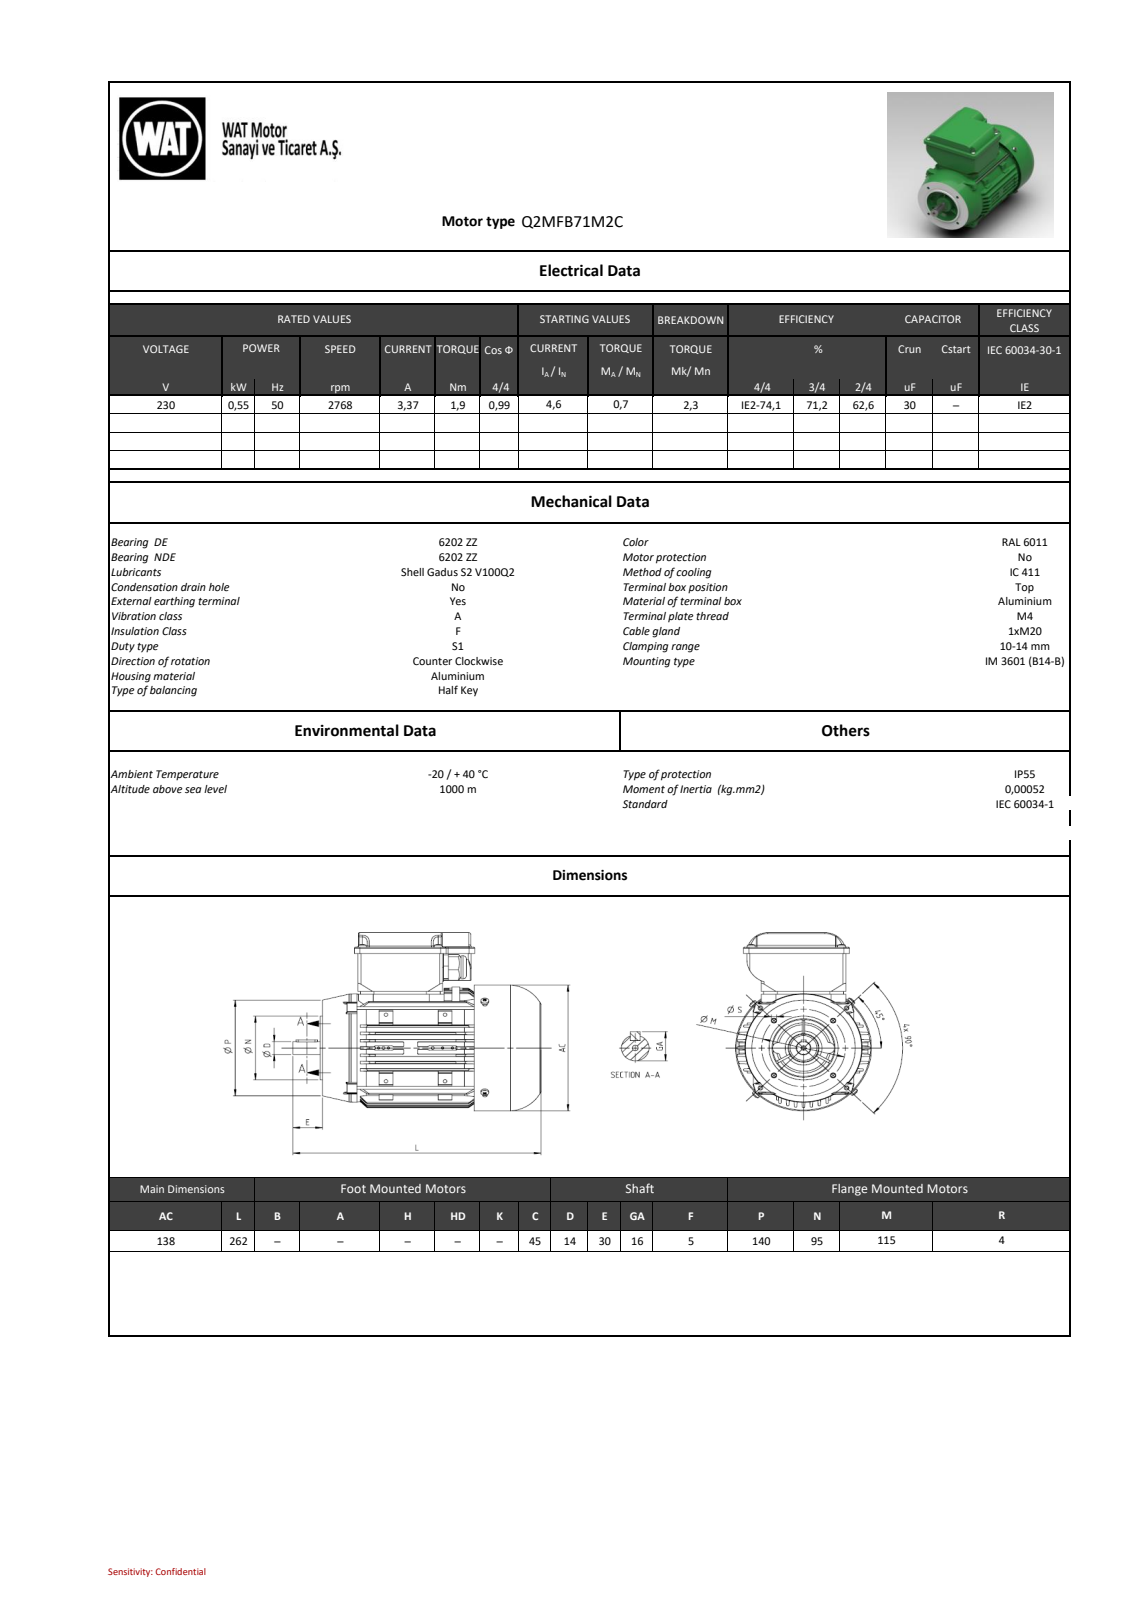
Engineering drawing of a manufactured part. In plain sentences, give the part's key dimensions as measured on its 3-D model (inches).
The part is named "BY6434017xx_004-TK_QM63-80; BY6424130xx_004-TKK_QM63-80; BY6422457xx_005-MOTOR_KAPAGI_QS71FB_ISLEME; 641304741_AZ-KAMA PARALEL A 5x5x22 St50 DIN6885 (+6 more)". Its 3-D file was written by "SIEMENS PLM Software NX2206.8101 (AUTOMOTIVE_DESIGN)". It is 24 solids with 2559 faces: 1236 planar, 703 cylindrical and 620 other. Overall it measures 10.315 by 7.746 by 5.531 inches. Its volume is 48.03 cubic inches and its surface area 752.5 square inches. Round holes: 8 of diameter 0.144, 8 of diameter 0.157, 8 of diameter 0.177, 6 of diameter 0.098, 5 of diameter 0.13, 5 of diameter 0.315, 4 of diameter 0.183, 4 of diameter 0.189, 3 of diameter 0.118, 3 of diameter 0.146, 2 of diameter 0.181, 1 of diameter 0.197. Round bosses or shafts: 8 of diameter 0.315, 8 of diameter 0.157, 8 of diameter 0.118, 4 of diameter 0.13, 1 of diameter 5.531, 1 of diameter 5.433, 1 of diameter 4.528, 1 of diameter 3.74. Partial cylindrical surfaces (rounded edges, fillets, slot ends): 103 of radius 0.039, 73 of radius 0.079, 36 of radius 0.047, 32 of radius 0.02, 18 of radius 0.197, 16 of radius 0.394, 14 of radius 0.098, 12 of radius 0.012. The main face-to-face distances are 0.118, 7.657, 6.24, 0.272, 7.776, 1.264, 1.417, 2.539, 0.079, 0.039. The hole center spacings are 3.322, 3.326, 3.442, 2.165, 1.441, 2.362, 0.168, 0.172.
